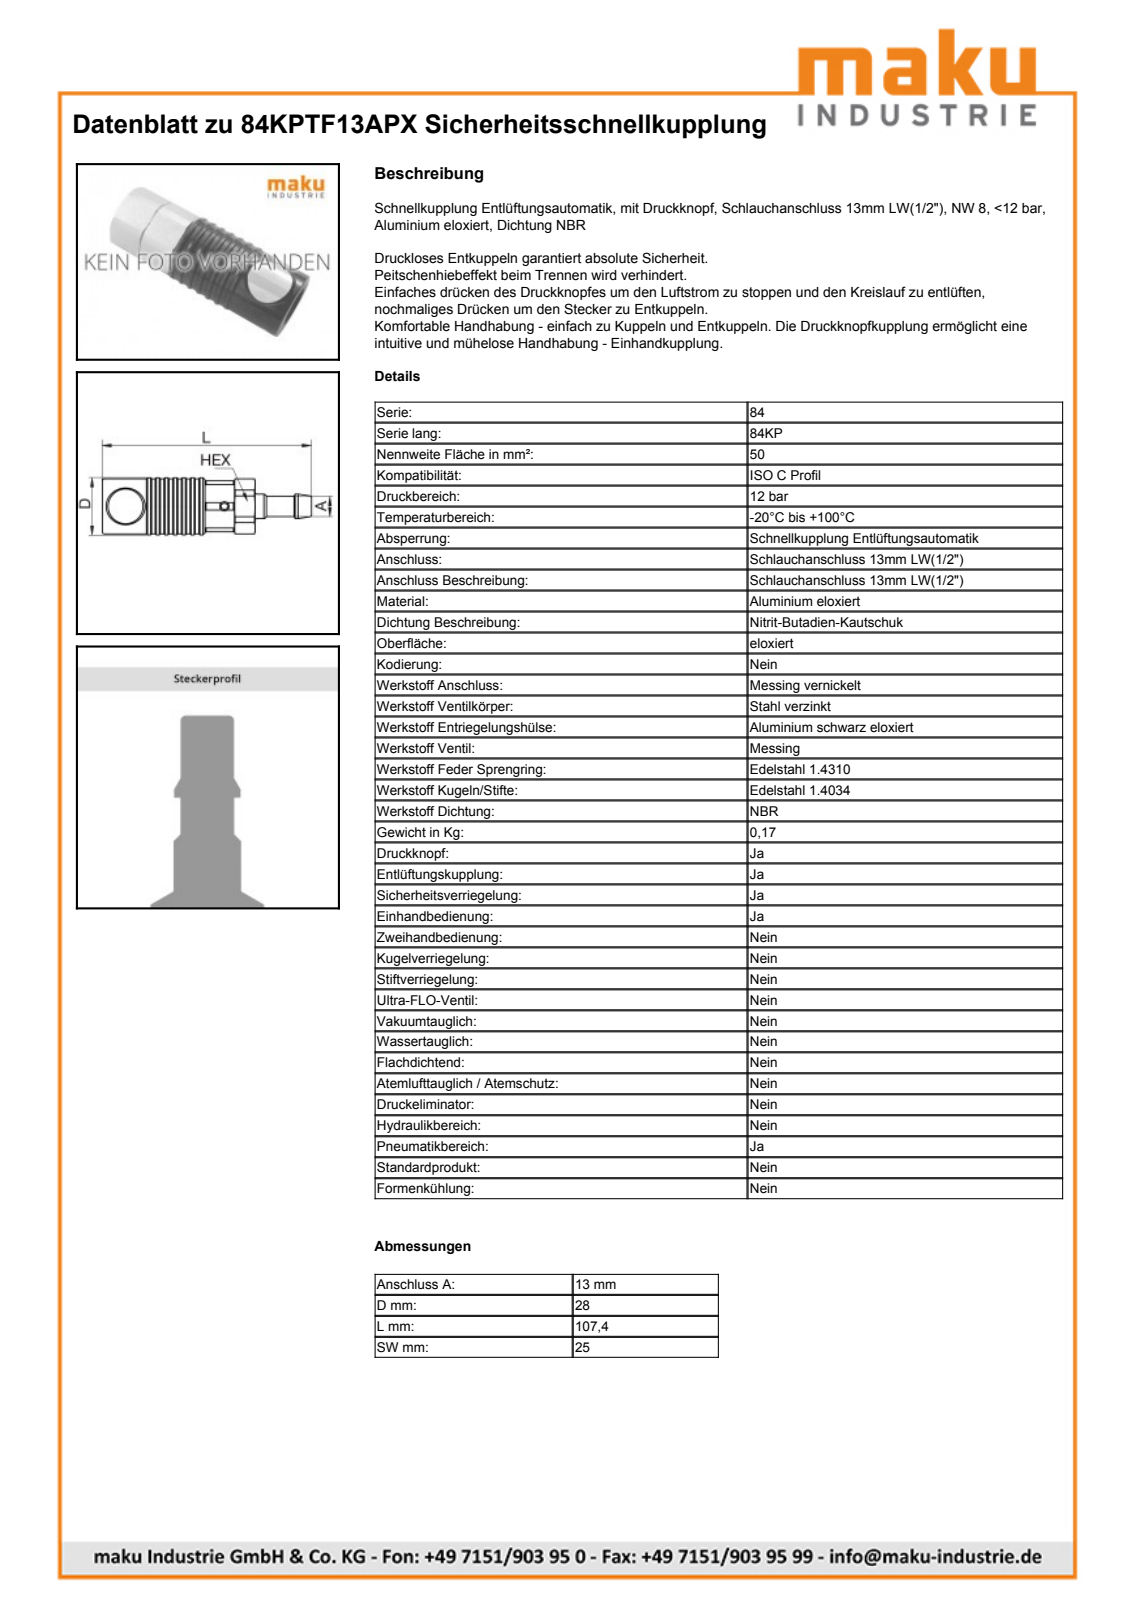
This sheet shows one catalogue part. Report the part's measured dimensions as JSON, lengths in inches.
{"part_name": "84KPTF13APX", "step_written_by": "Autodesk Inventor 2019 (CONFIG_CONTROL_DESIGN)", "units": "inches", "bodies": {"solids": 33, "faces": 345, "planar": 114, "cylindrical": 120, "other": 111}, "overall_size": [4.228, 1.102, 1.102], "volume_in3": 3.674, "surface_area_in2": 52.63, "round_holes": [[0.138, 2], [0.157, 2], [0.551, 2], [0.311, 1], [0.315, 1], [0.394, 1], [0.441, 1], [0.555, 1], [0.61, 1], [0.657, 1], [0.659, 1], [0.673, 1]], "round_bosses_or_shafts": [[1.102, 1], [1.063, 1], [0.984, 1], [0.919, 1], [0.917, 1], [0.906, 1], [0.857, 1], [0.776, 1]], "partial_cylinders_radius": [[0.218, 1], [0.335, 1], [0.366, 1], [0.384, 1], [0.531, 1], [0.571, 1]], "face_to_face_distances": [0.984, 0.394, 2.535, 1.39, 1.146, 1.35, 0.957, 0.252, 0.894, 1.642], "hole_center_spacings": [0.047, 0.051, 0.866, 1.028, 1.894]}
